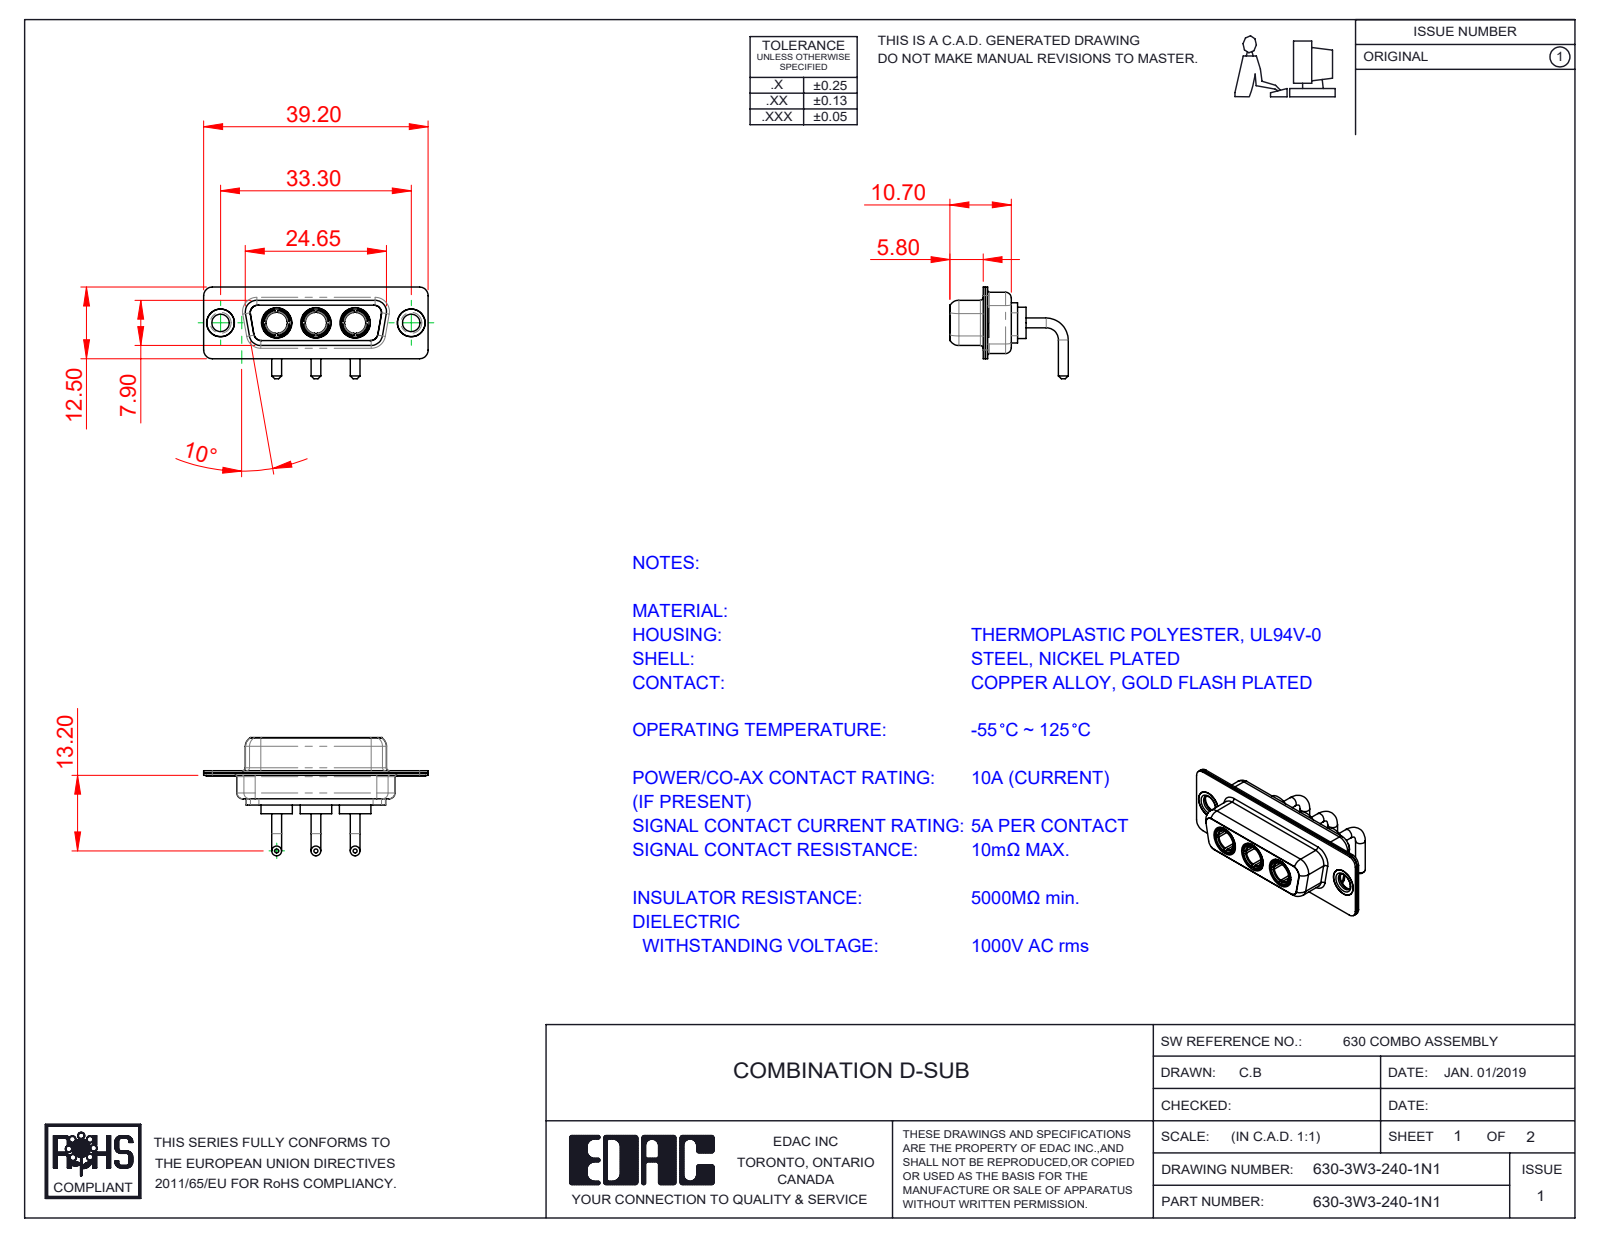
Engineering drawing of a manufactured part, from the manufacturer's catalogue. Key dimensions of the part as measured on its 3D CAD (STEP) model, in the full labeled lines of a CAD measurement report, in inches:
Part name (STEP PRODUCT): 630Combo Thru Hole Rivet; 630Combo Housing_3W3; Power Socket_10A RA; 630Combo Shell Rear_15 Contacts (+2 more)
STEP written by: SolidWorks 2020 (CONFIG_CONTROL_DESIGN)
Units: inches
Bodies: 11 solids, 487 faces (154 planar, 196 cylindrical, 137 other)
Overall size (bounding box): 1.543 × 0.813 × 0.63
Volume: 0.146 in³ · Surface area: 8.722 in²
Round holes (diameter × count): ⌀0.191 ×5, ⌀0.146 ×3, ⌀0.209 ×3, ⌀0.12 ×2, ⌀0.157 ×2, ⌀0.159 ×2
Round bosses / shafts (diameter × count): ⌀0.067 ×6, ⌀0.217 ×3, ⌀0.205 ×3, ⌀0.195 ×3, ⌀0.187 ×3, ⌀0.148 ×3, ⌀0.197 ×2, ⌀0.195 ×2
Partial cylindrical surfaces — rounded edges, fillets, slot ends (radius × count): R0.059 ×16, R0.053 ×12, R0.079 ×12, R0.063 ×8, R0.01 ×4, R0.02 ×4, R0.024 ×4, R0.026 ×4
Main face-to-face distances: 0.016, 0.018, 0.055, 0.333, 0.35, 0.071, 0.031, 0.278, 0.295, 0.244
Hole centre spacings: 0.27, 0.386, 0.656, 0.925, 0.539, 1.311
